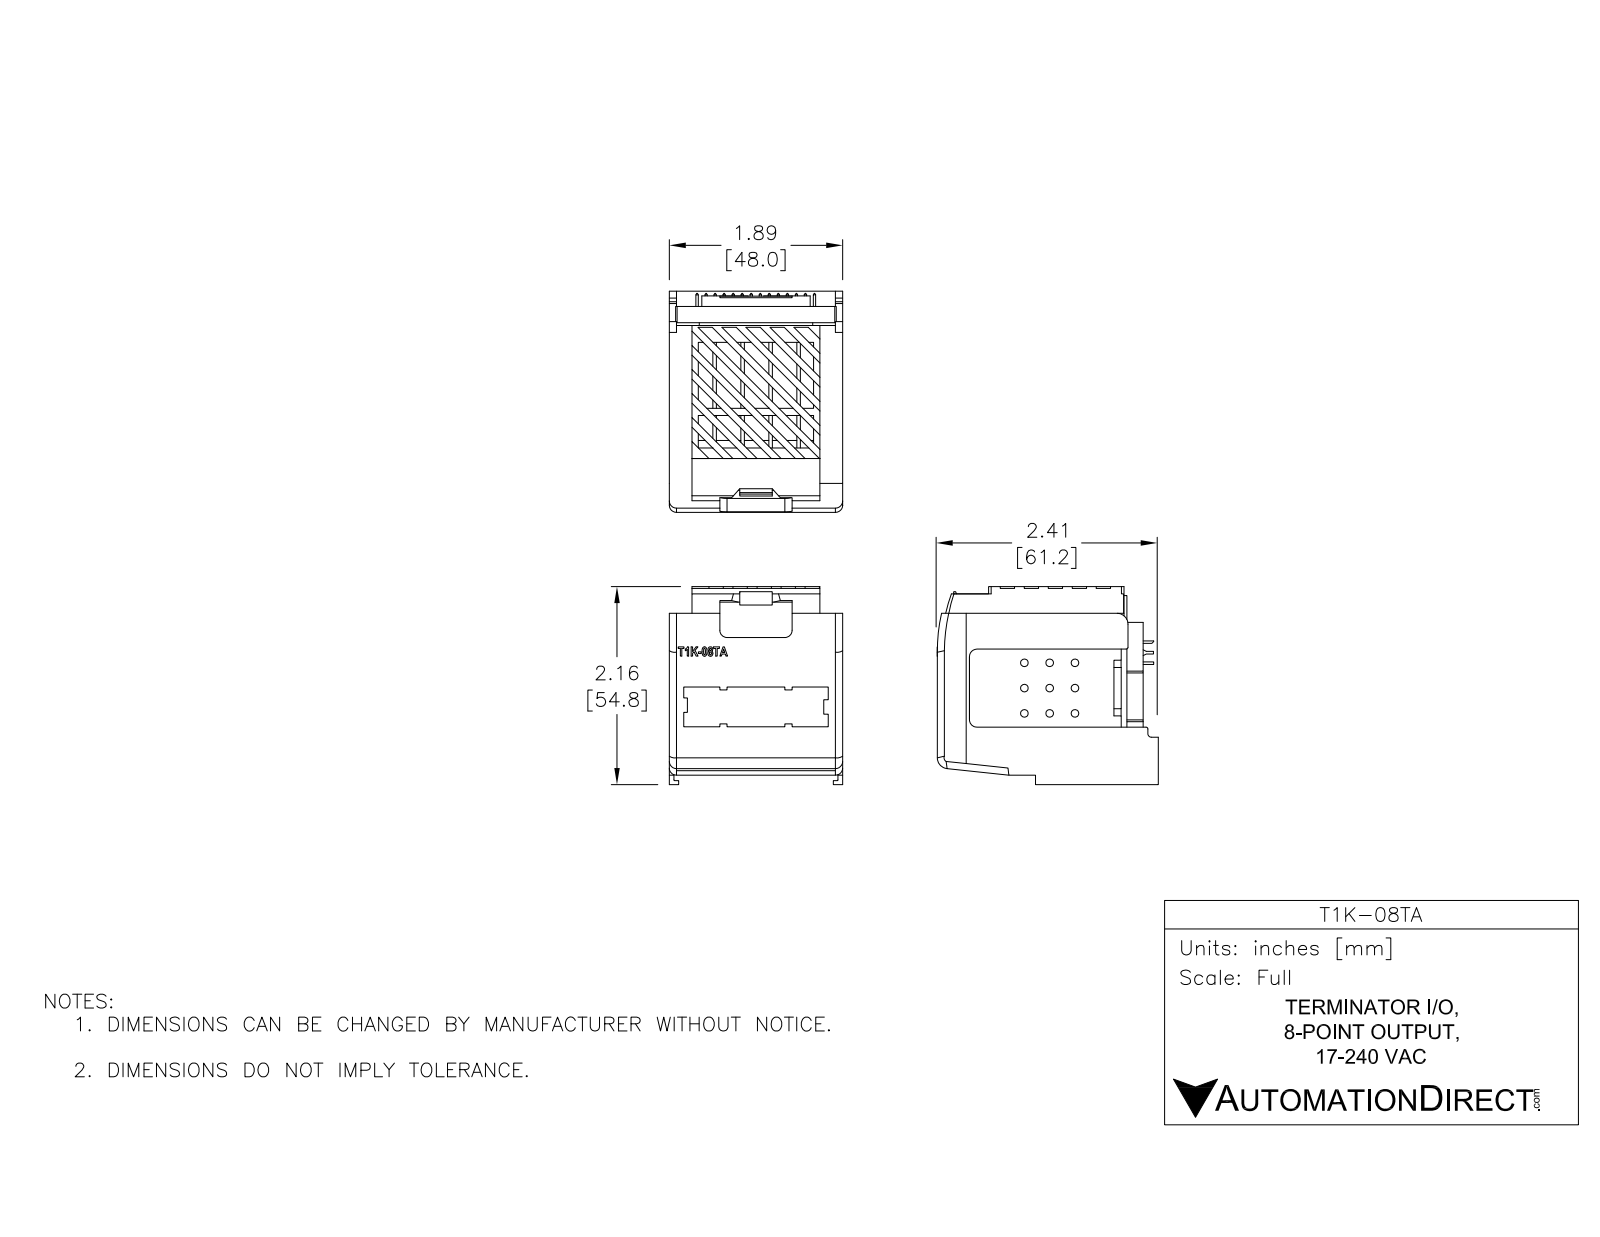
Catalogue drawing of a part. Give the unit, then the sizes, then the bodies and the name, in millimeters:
Units: millimetres
Overall size (bounding box): 65.1 × 61.36 × 47.6
Round holes (diameter × count): ⌀3 ×8
Round bosses / shafts (diameter × count): ⌀0.7 ×28
Partial cylindrical surfaces — rounded edges, fillets, slot ends (radius × count): R3.5 ×10, R1 ×5, R0.25 ×3, R0.55 ×3, R1.5 ×2, R8 ×1, R10 ×1, R18 ×1
Main face-to-face distances: 2, 45.6, 47.6, 43.6, 55.35, 49.9, 6.55, 39.05, 59.8, 9.9
Hole centre spacings: 5.2, 10.4, 15.6, 20.8, 26, 31.2, 36.4
Volume: 30 279 mm³ · Surface area: 35 941 mm²
Bodies: 1 solid, 542 faces (413 planar, 101 cylindrical, 28 other)
Part name (STEP PRODUCT): T1K-08TA
STEP written by: SolidWorks 2013 (AUTOMOTIVE_DESIGN)
